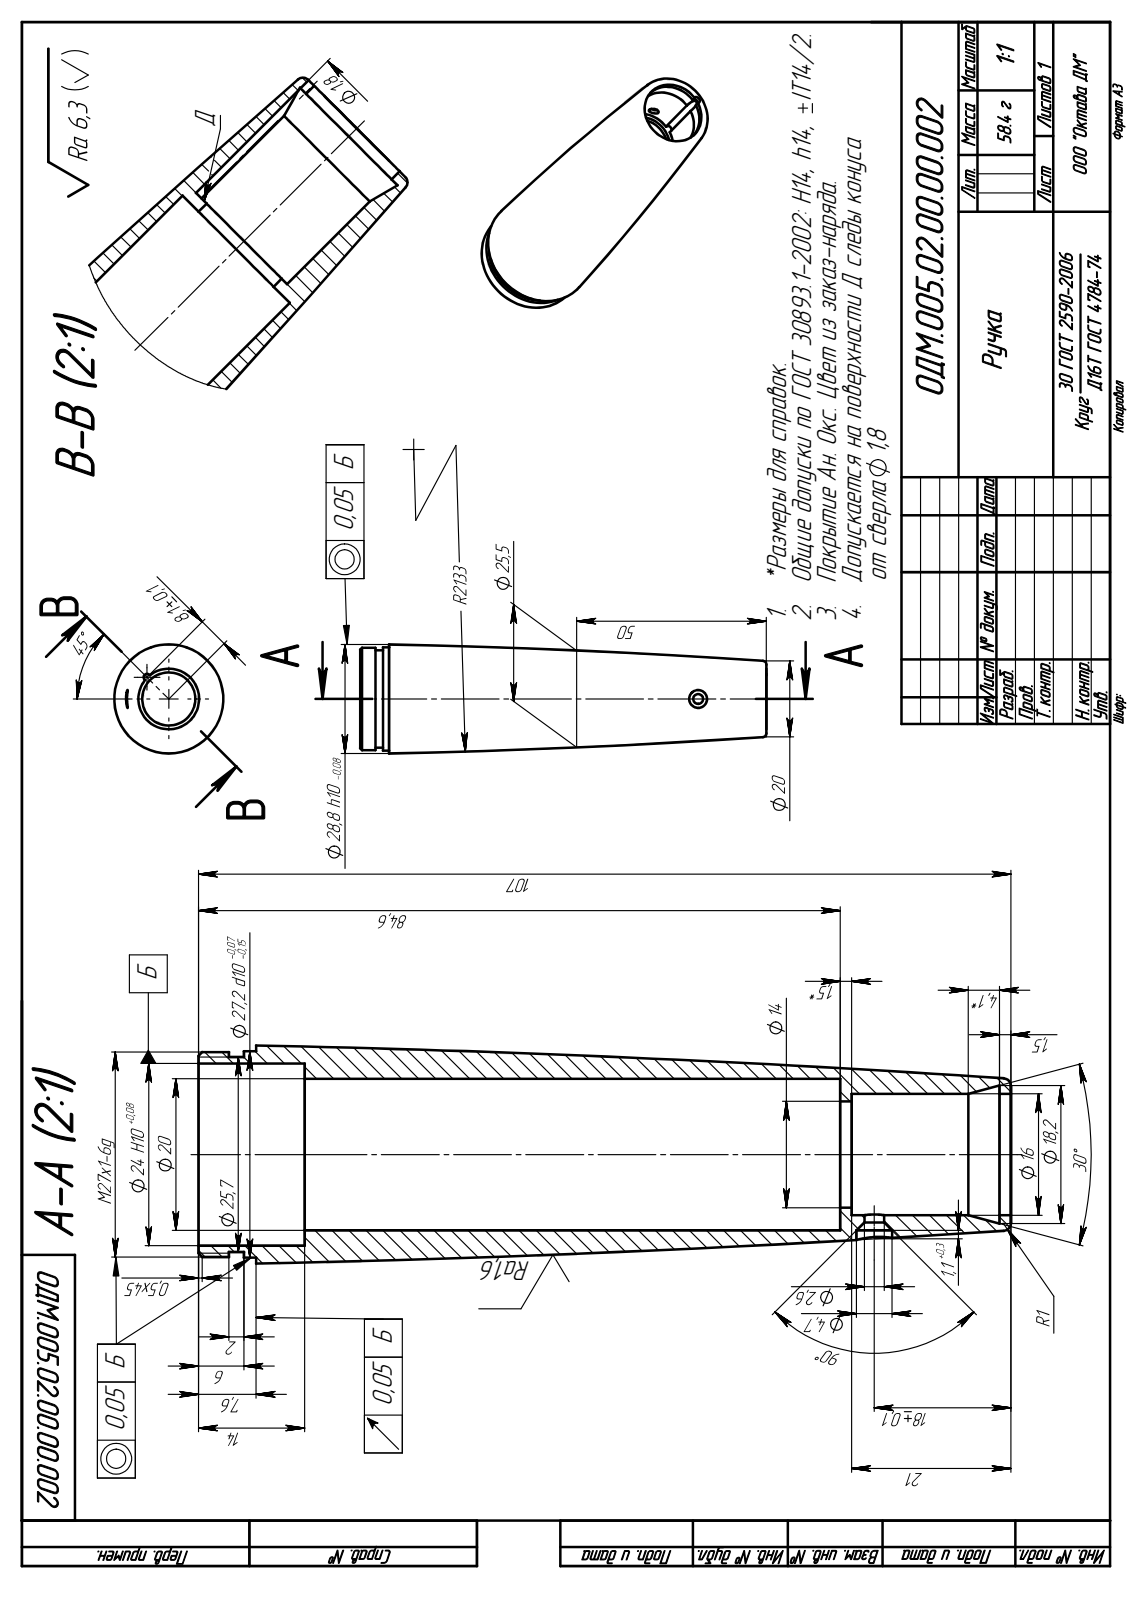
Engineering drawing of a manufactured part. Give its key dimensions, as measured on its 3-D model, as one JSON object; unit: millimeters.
{"part_name": "ОДМ.005.02.00.00.002 Ручка", "step_written_by": "SolidWorks 2017 (AUTOMOTIVE_DESIGN)", "units": "millimeters", "bodies": {"solids": 1, "faces": 43, "planar": 8, "cylindrical": 24, "other": 11}, "overall_size": [107.11, 28.76, 28.75], "volume_mm3": 20992, "surface_area_mm2": 15954, "round_holes": [[2.6, 1], [4.7, 1], [14, 1], [16, 1], [20, 1], [24, 1]], "round_bosses_or_shafts": [[27.2, 1], [27, 1], [25.7, 1]], "partial_cylinders_radius": [[0.9, 1]], "face_to_face_distances": [70.61, 14, 84.61, 7.6, 6.4, 77.01, 6, 1.6, 8, 78.61]}
